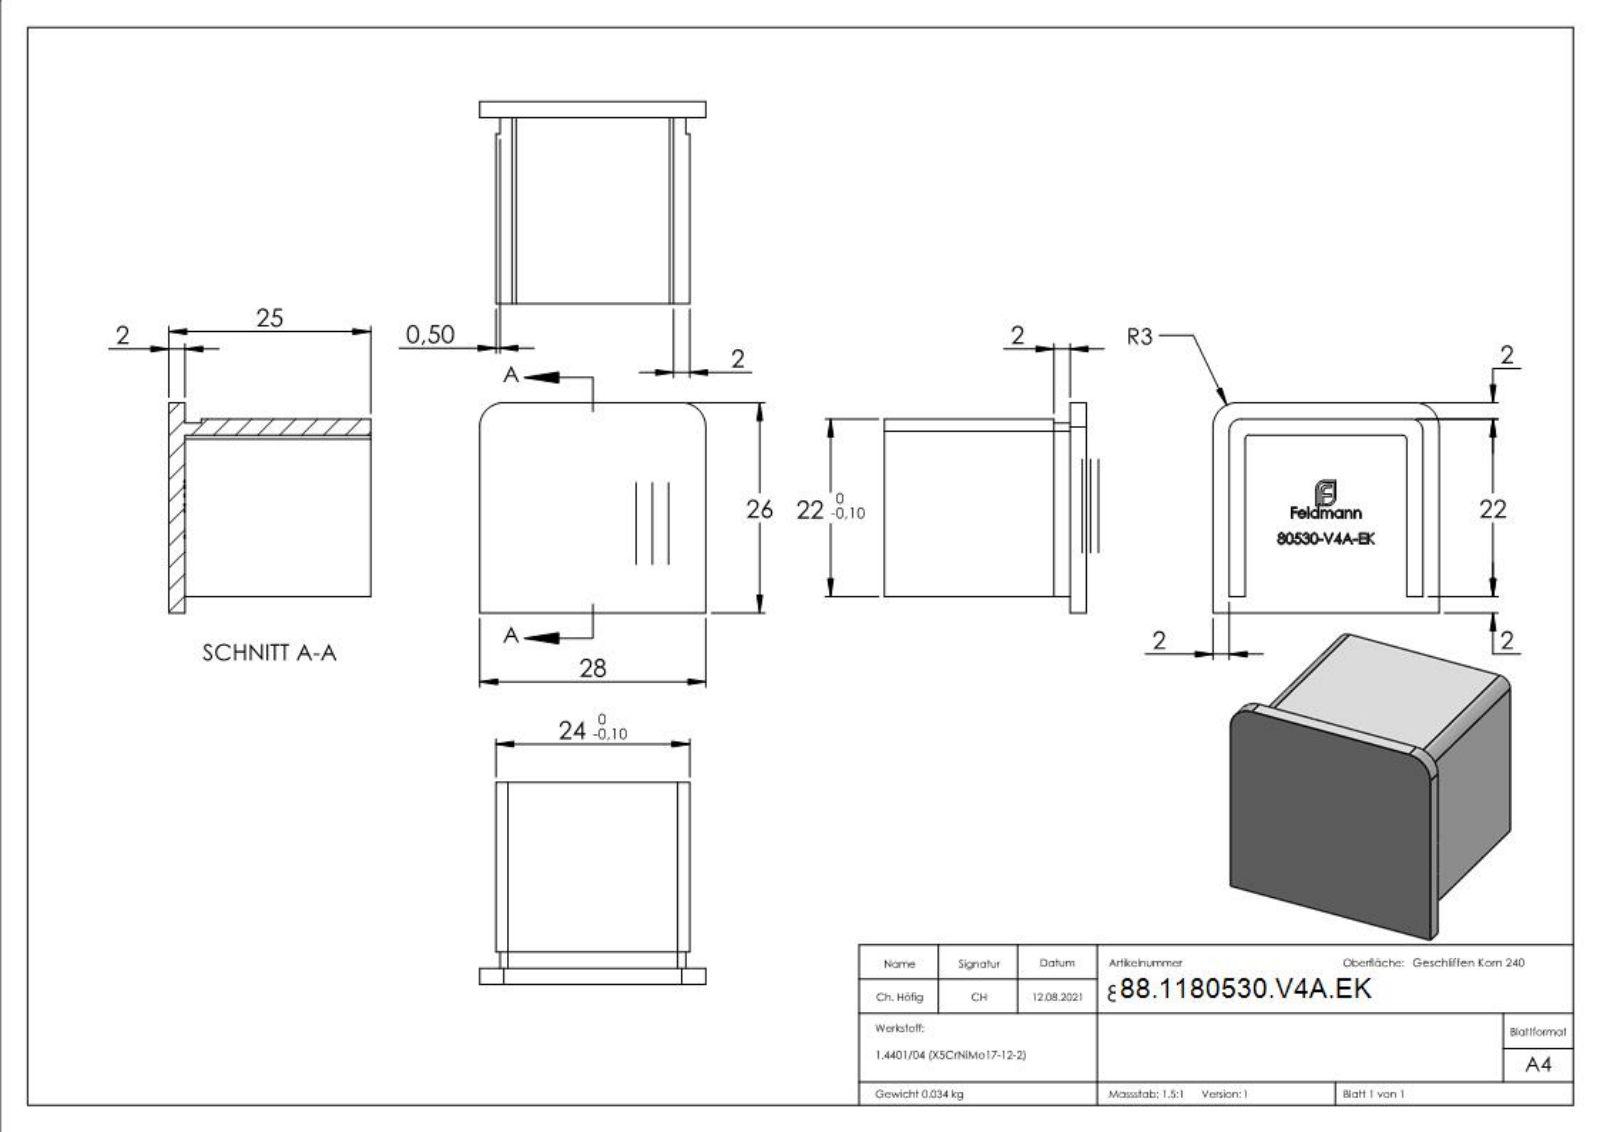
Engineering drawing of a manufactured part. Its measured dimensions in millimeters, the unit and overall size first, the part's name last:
Units: millimetres
Overall size (bounding box): 28 × 26 × 25
Partial cylindrical surfaces — rounded edges, fillets, slot ends (radius × count): R0.5 ×2, R1 ×2, R1.5 ×2, R3 ×2
Main face-to-face distances: 2, 22, 24, 20, 4, 23, 26, 25, 1.5, 2.5
Volume: 4 306 mm³ · Surface area: 4 730 mm²
Bodies: 1 solid, 333 faces (200 planar, 8 cylindrical, 125 other)
Part name (STEP PRODUCT): 80530-V4A-EK
STEP written by: SolidWorks 2018 (CONFIG_CONTROL_DESIGN)
